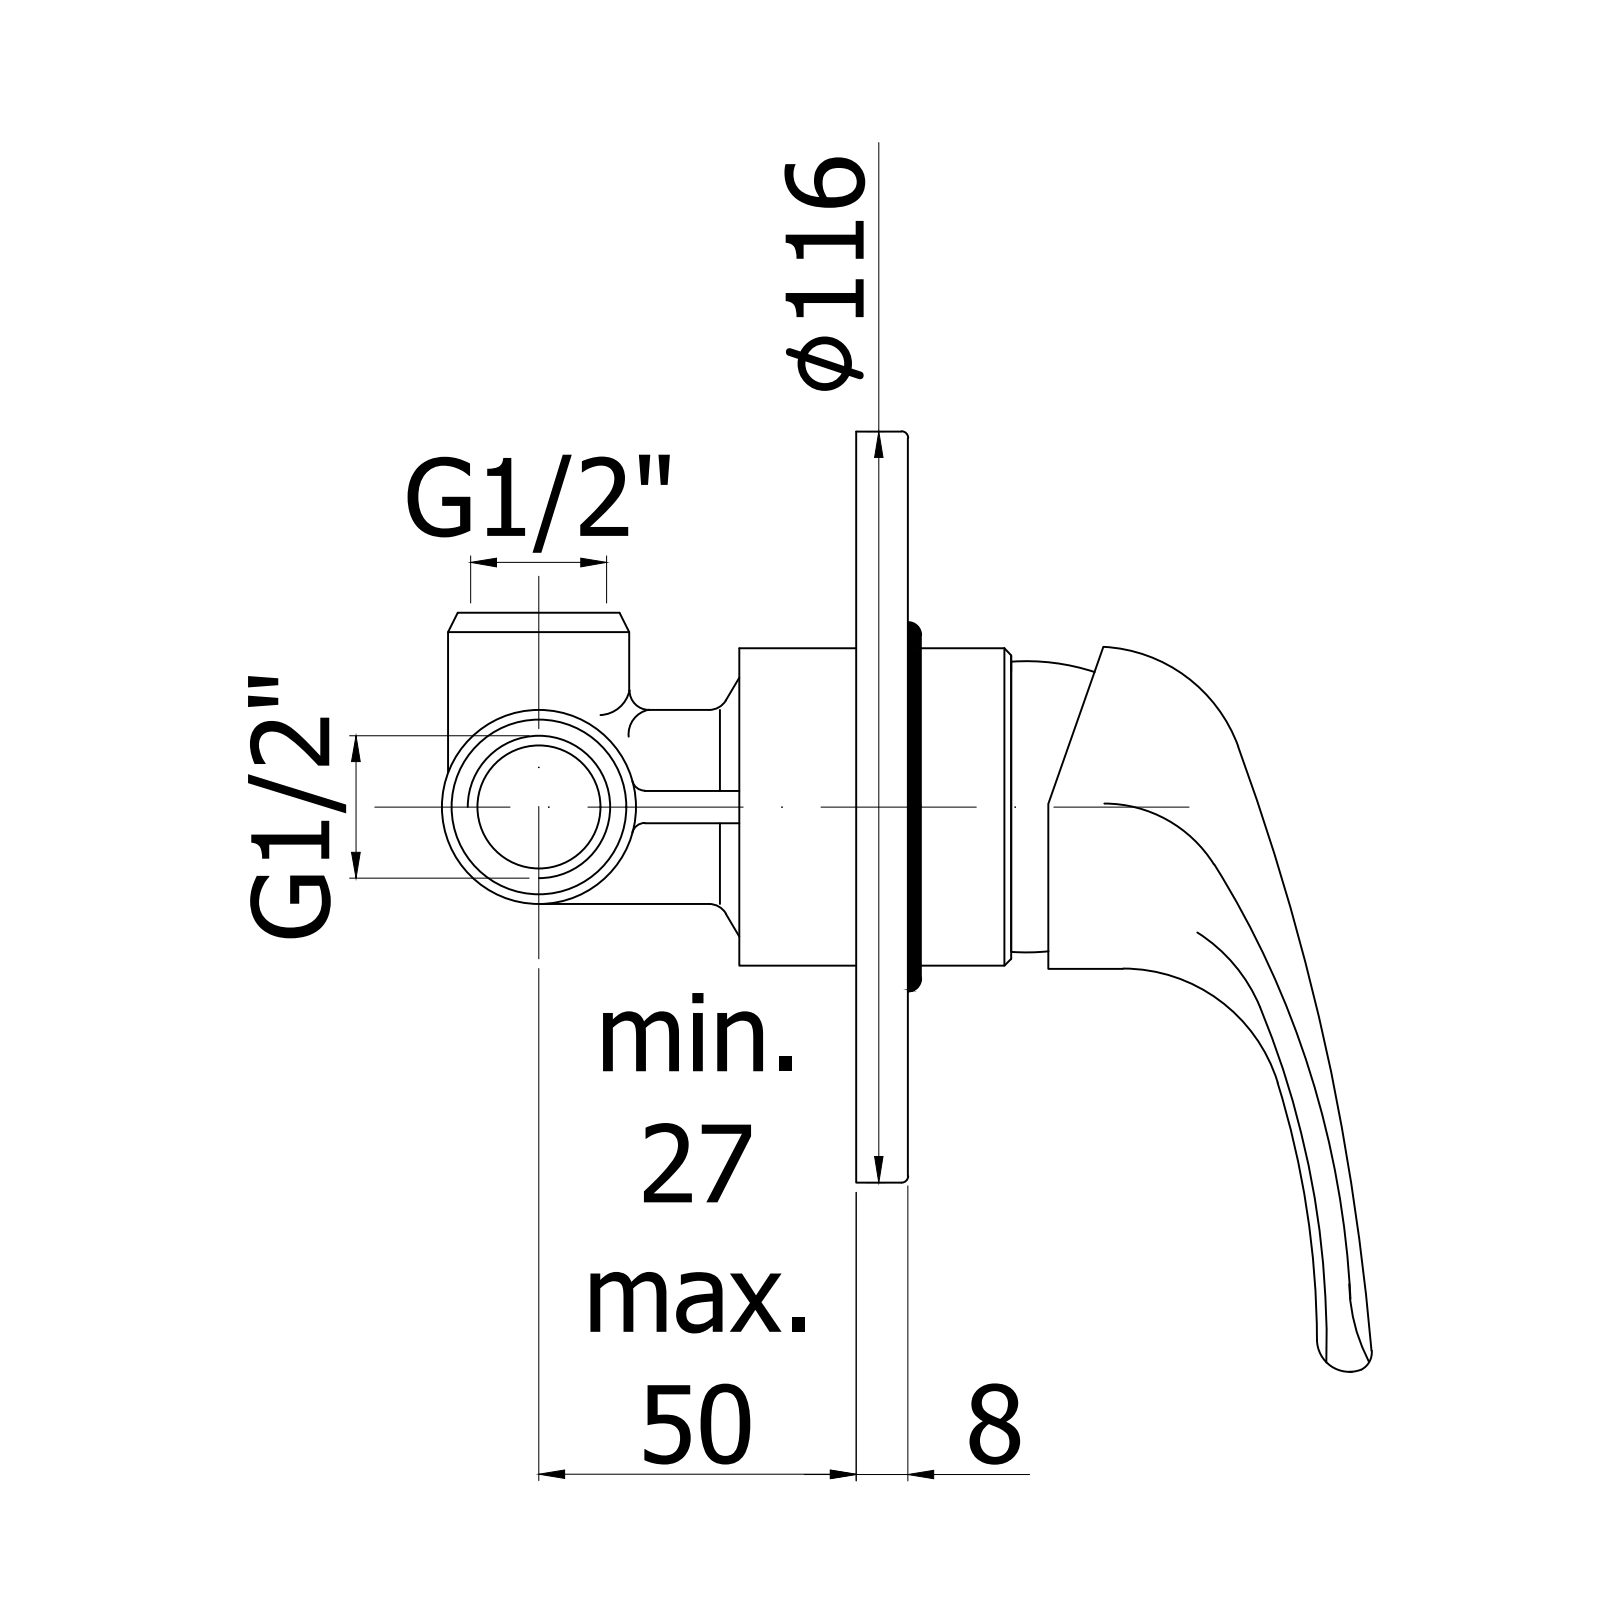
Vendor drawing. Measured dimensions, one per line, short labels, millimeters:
name: ND010CR
written by: CREO PARAMETRIC BY PTC INC, 2020044 (CONFIG_CONTROL_DESIGN)
unit: mm
bodies: 1 solid, 73 faces (29 planar, 14 cylindrical, 30 other)
size: 146.32 × 116 × 89.5
volume: 191 748 mm³; area: 43 301 mm²
holes: 1× ⌀6
bosses: 1× ⌀116, 1× ⌀56.5, 1× ⌀50
rounds: 1× R3.9, 1× R4
face distances: 45.5, 11, 34.5, 59.75, 48.75, 14.25, 15.3, 18.1, 31, 20
